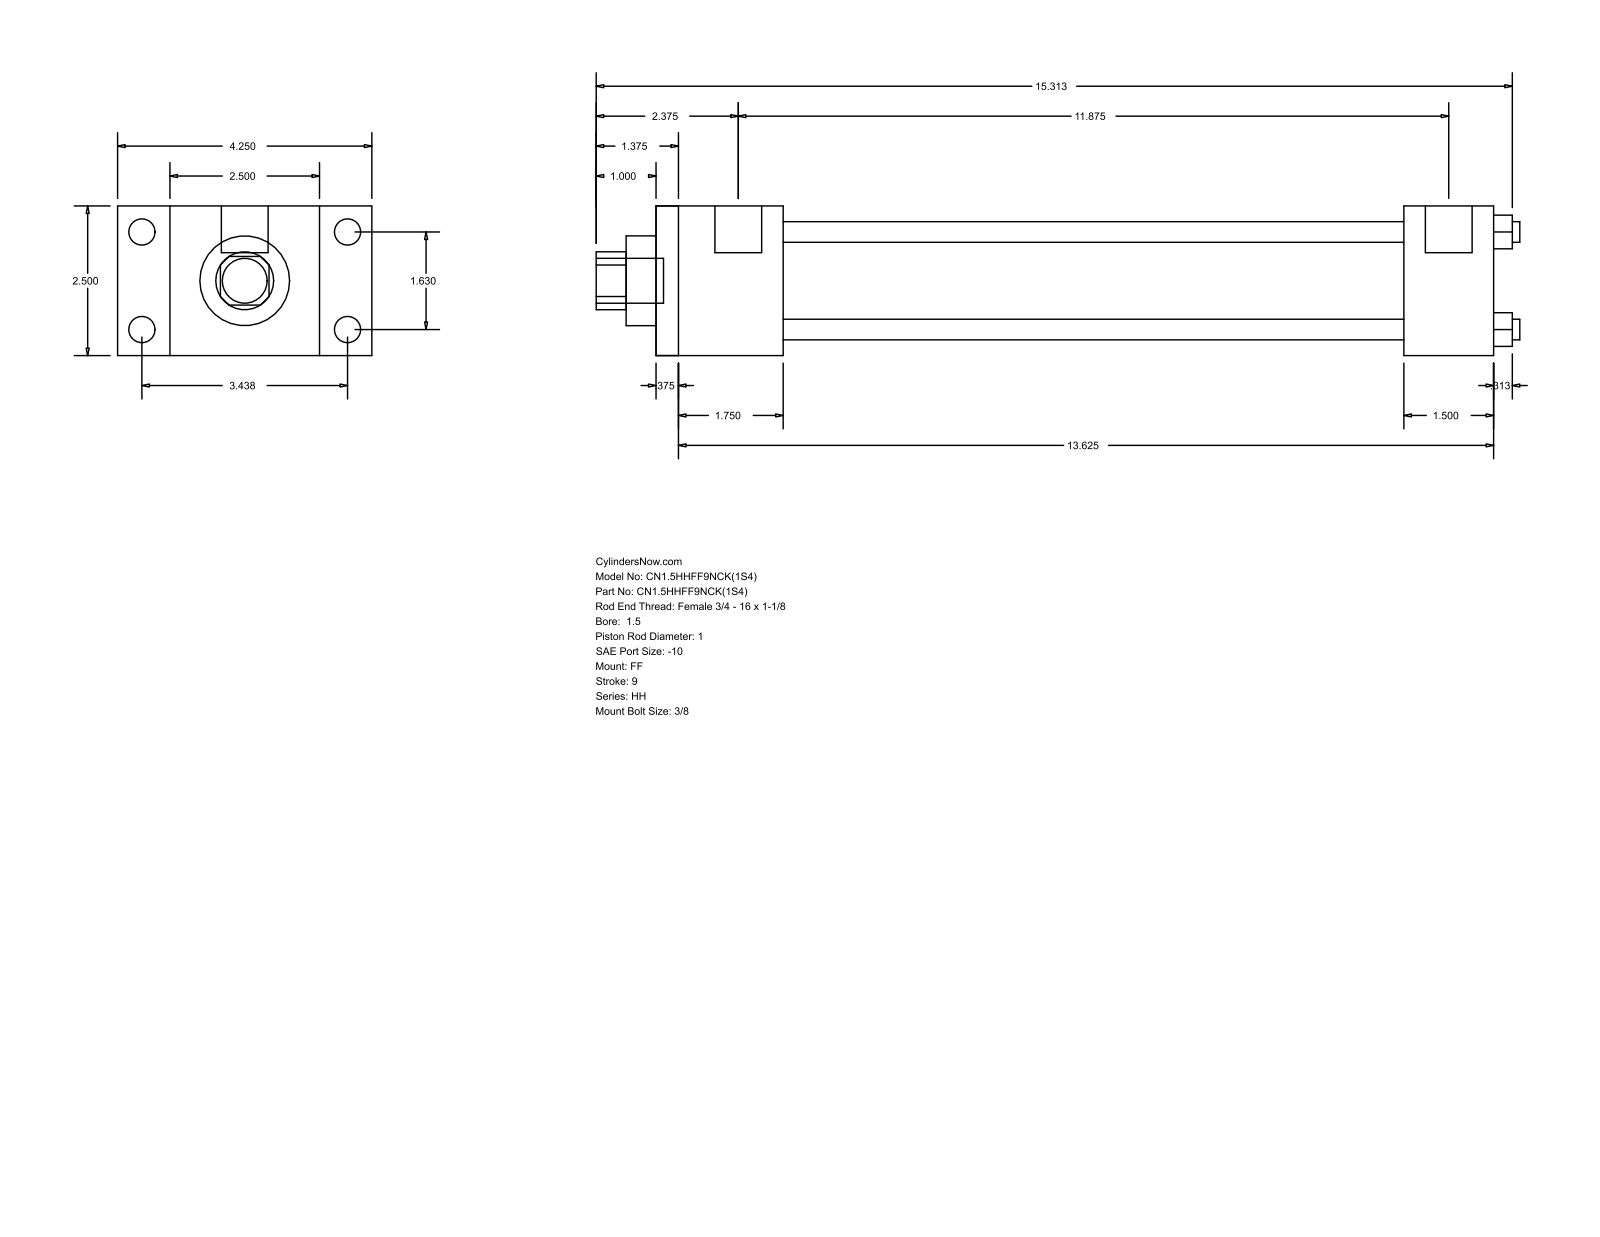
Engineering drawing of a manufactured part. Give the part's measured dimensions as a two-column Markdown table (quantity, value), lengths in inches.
| quantity | value |
| --- | --- |
| part name | HH_FF__0150_1 |
| STEP written by | GSSL Pune (CONFIG_CONTROL_DESIGN) |
| units | inches |
| bodies | 0 solids, 92 faces (64 planar, 28 cylindrical, 0 other) |
| overall size | 15.437 × 4.25 × 2.5 |
| round holes (diameter × count) | 0.345 × 4, 1 × 1, 1.5 × 1, 1.75 × 1 |
| round bosses / shafts (diameter × count) | 0.438 × 4, 0.219 × 4, 0.781 × 2, 0.75 × 1 |
| partial cylindrical surfaces (radius × count) | 0.484 × 1 |
| main face-to-face distances | 2.5, 14, 0.375, 13.625, 2.125, 1.75, 11.875, 12.5, 12.125, 10.375 |
| hole center spacings | 1.152, 1.63, 2.305 |
